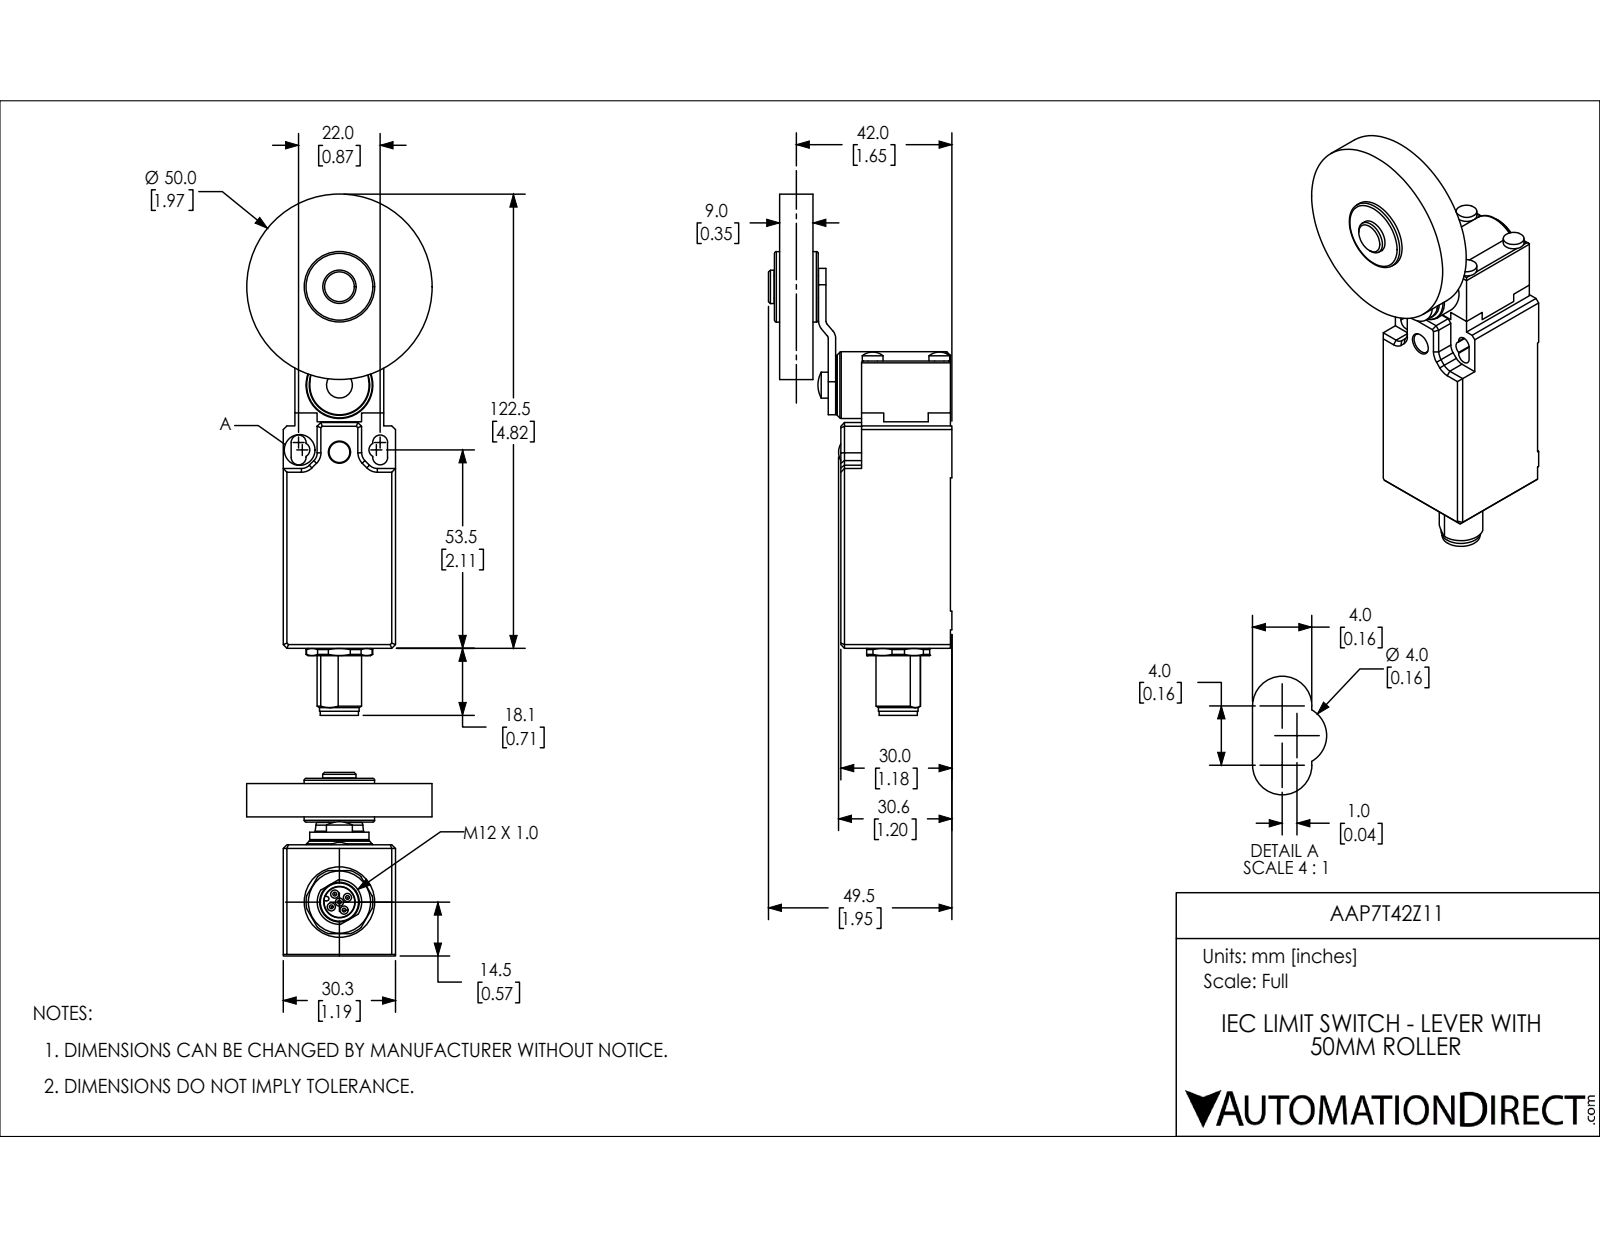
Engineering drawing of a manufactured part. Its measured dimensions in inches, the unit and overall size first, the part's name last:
Units: inches
Overall size (bounding box): 5.535 × 1.969 × 1.949
Round holes (diameter × count): ⌀0.087 ×5, ⌀0.236 ×1, ⌀0.512 ×1, ⌀0.551 ×1, ⌀0.63 ×1
Round bosses / shafts (diameter × count): ⌀0.22 ×5, ⌀0.055 ×5, ⌀0.039 ×5, ⌀1.969 ×1, ⌀0.748 ×1, ⌀0.709 ×1, ⌀0.587 ×1, ⌀0.531 ×1
Partial cylindrical surfaces — rounded edges, fillets, slot ends (radius × count): R0.079 ×6, R0.118 ×6, R0.02 ×4, R0.039 ×2, R0.024 ×1, R0.197 ×1, R0.236 ×1, R0.315 ×1
Main face-to-face distances: 0.354, 1.815, 1.461, 0.65, 1.193, 1.165, 0.295, 0.055, 0.124, 1.069
Hole centre spacings: 0.098, 0.139, 0.197
Volume: 5.232 in³ · Surface area: 35.49 in²
Bodies: 4 solids, 344 faces (151 planar, 131 cylindrical, 62 other)
Part name (STEP PRODUCT): AAP7T42Z11
STEP written by: SolidWorks 2018 (AUTOMOTIVE_DESIGN)
